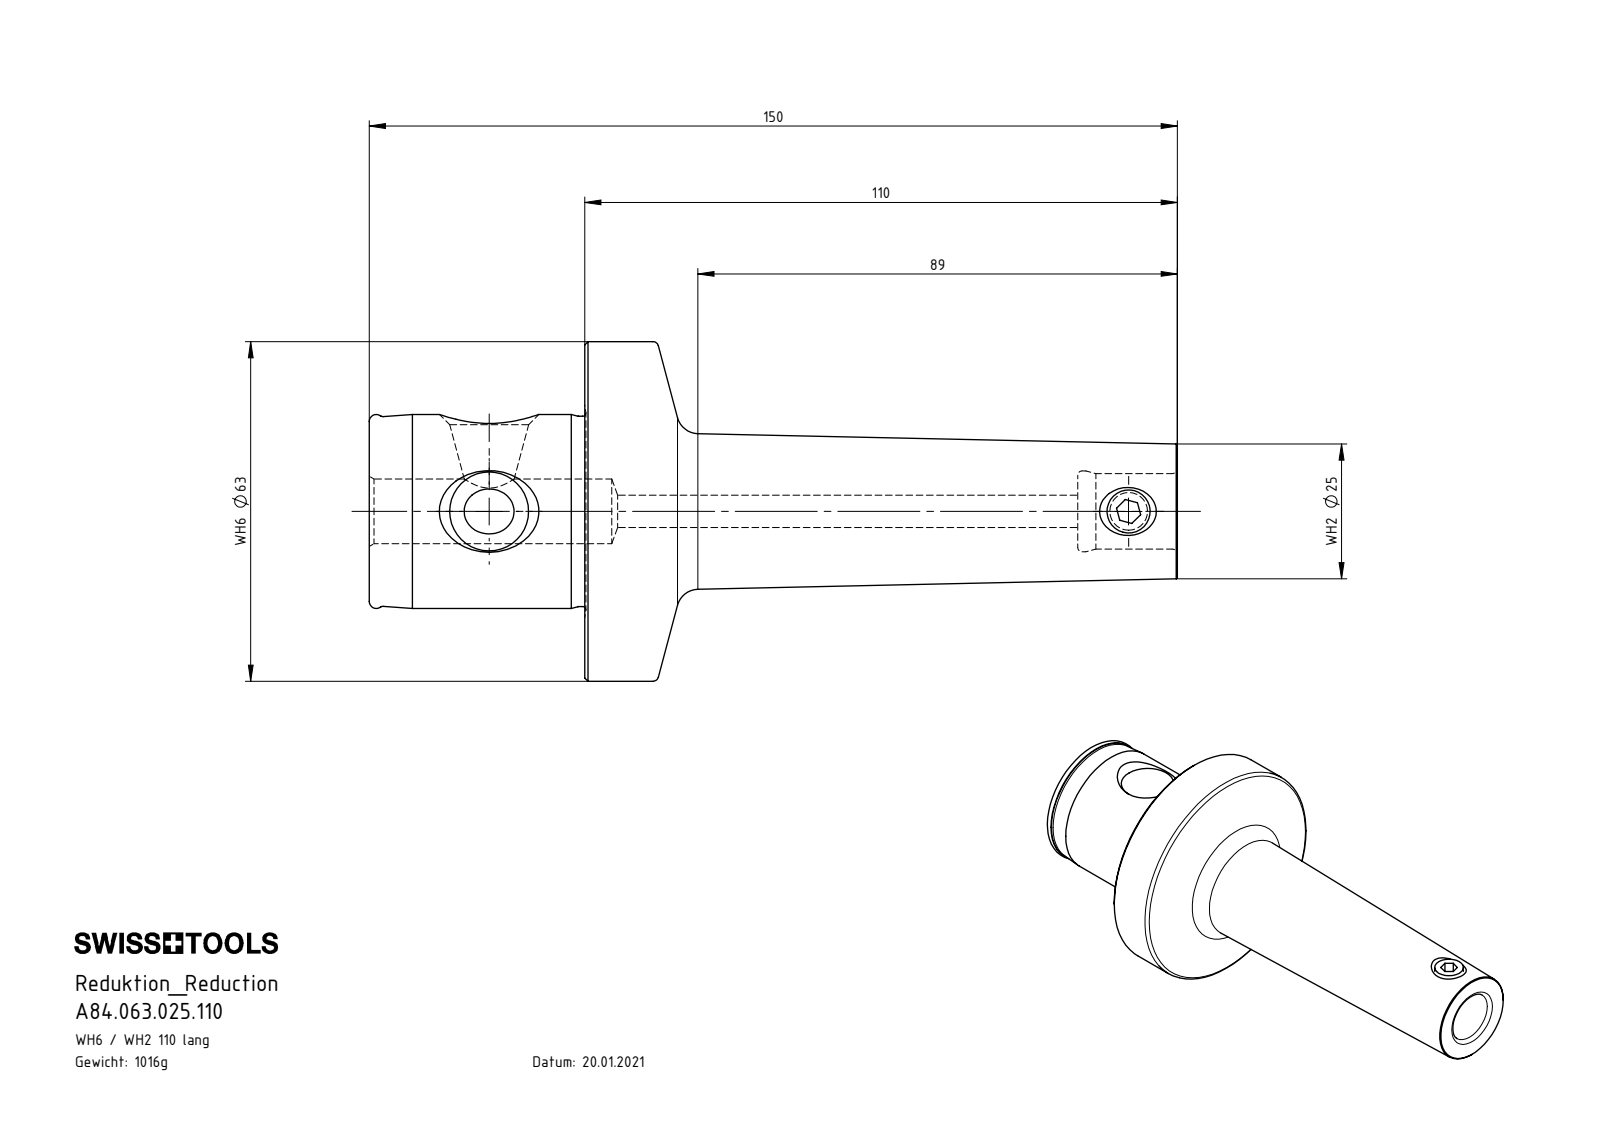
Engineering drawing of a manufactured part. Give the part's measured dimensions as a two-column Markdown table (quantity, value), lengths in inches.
| quantity | value |
| --- | --- |
| part name | WH2-ER1.001.010; A84.063.025.110; WH6-WH2.K01.110_B |
| STEP written by | SolidWorks 2017 (CONFIG_CONTROL_DESIGN) |
| units | inches |
| bodies | 2 solids, 87 faces (13 planar, 18 cylindrical, 56 other) |
| overall size | 5.906 × 2.48 × 2.48 |
| volume | 7.965 in³ |
| surface area | 39.57 in² |
| round holes (diameter × count) | 0.197 × 1, 0.276 × 1, 0.472 × 1, 0.551 × 1, 0.591 × 1 |
| round bosses / shafts (diameter × count) | 2.48 × 1, 1.417 × 1, 1.39 × 1, 0.315 × 1 |
| main face-to-face distances | 1.575, 5.906, 4.331, 5.177, 3.602, 0.728, 0.157, 0.197, 0.394 |
